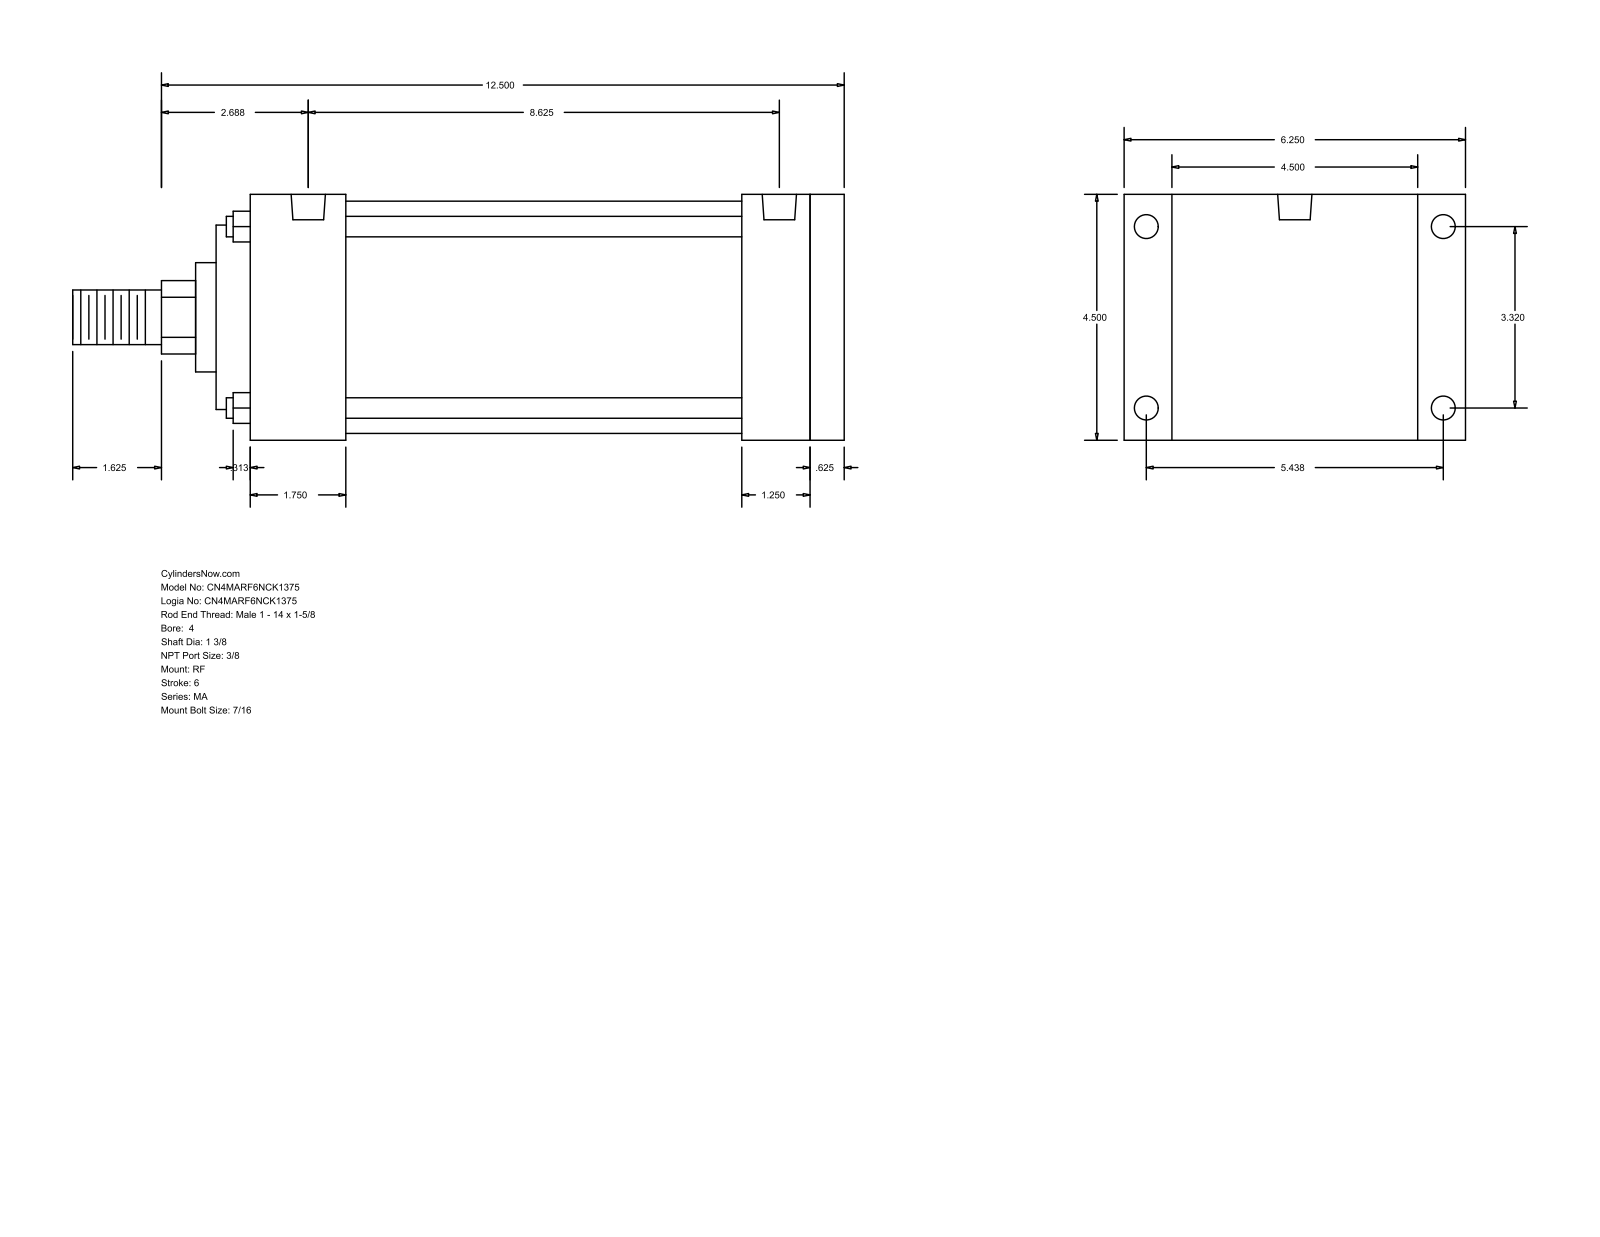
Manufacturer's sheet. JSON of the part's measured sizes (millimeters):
{"part_name": "MA_RF__0400_1.375", "step_written_by": "GSSL Pune (CONFIG_CONTROL_DESIGN)", "units": "millimeters", "bodies": {"solids": 0, "faces": 94, "planar": 65, "cylindrical": 29, "other": 0}, "overall_size": [358.77, 158.75, 114.3], "round_holes": [[11.11, 8], [15.93, 2]], "round_bosses_or_shafts": [[9.53, 4], [107.95, 1], [85.72, 1], [50.8, 1], [34.92, 1], [25.4, 1]], "partial_cylinders_radius": [[17.06, 1]], "face_to_face_distances": [114.3, 276.23, 15.88, 260.35, 15.87, 276.22, 292.1, 22.23, 136.53, 244.48], "hole_center_spacings": [4.77, 84.32, 138.12, 161.82, 209.54, 214.31, 219.08]}
